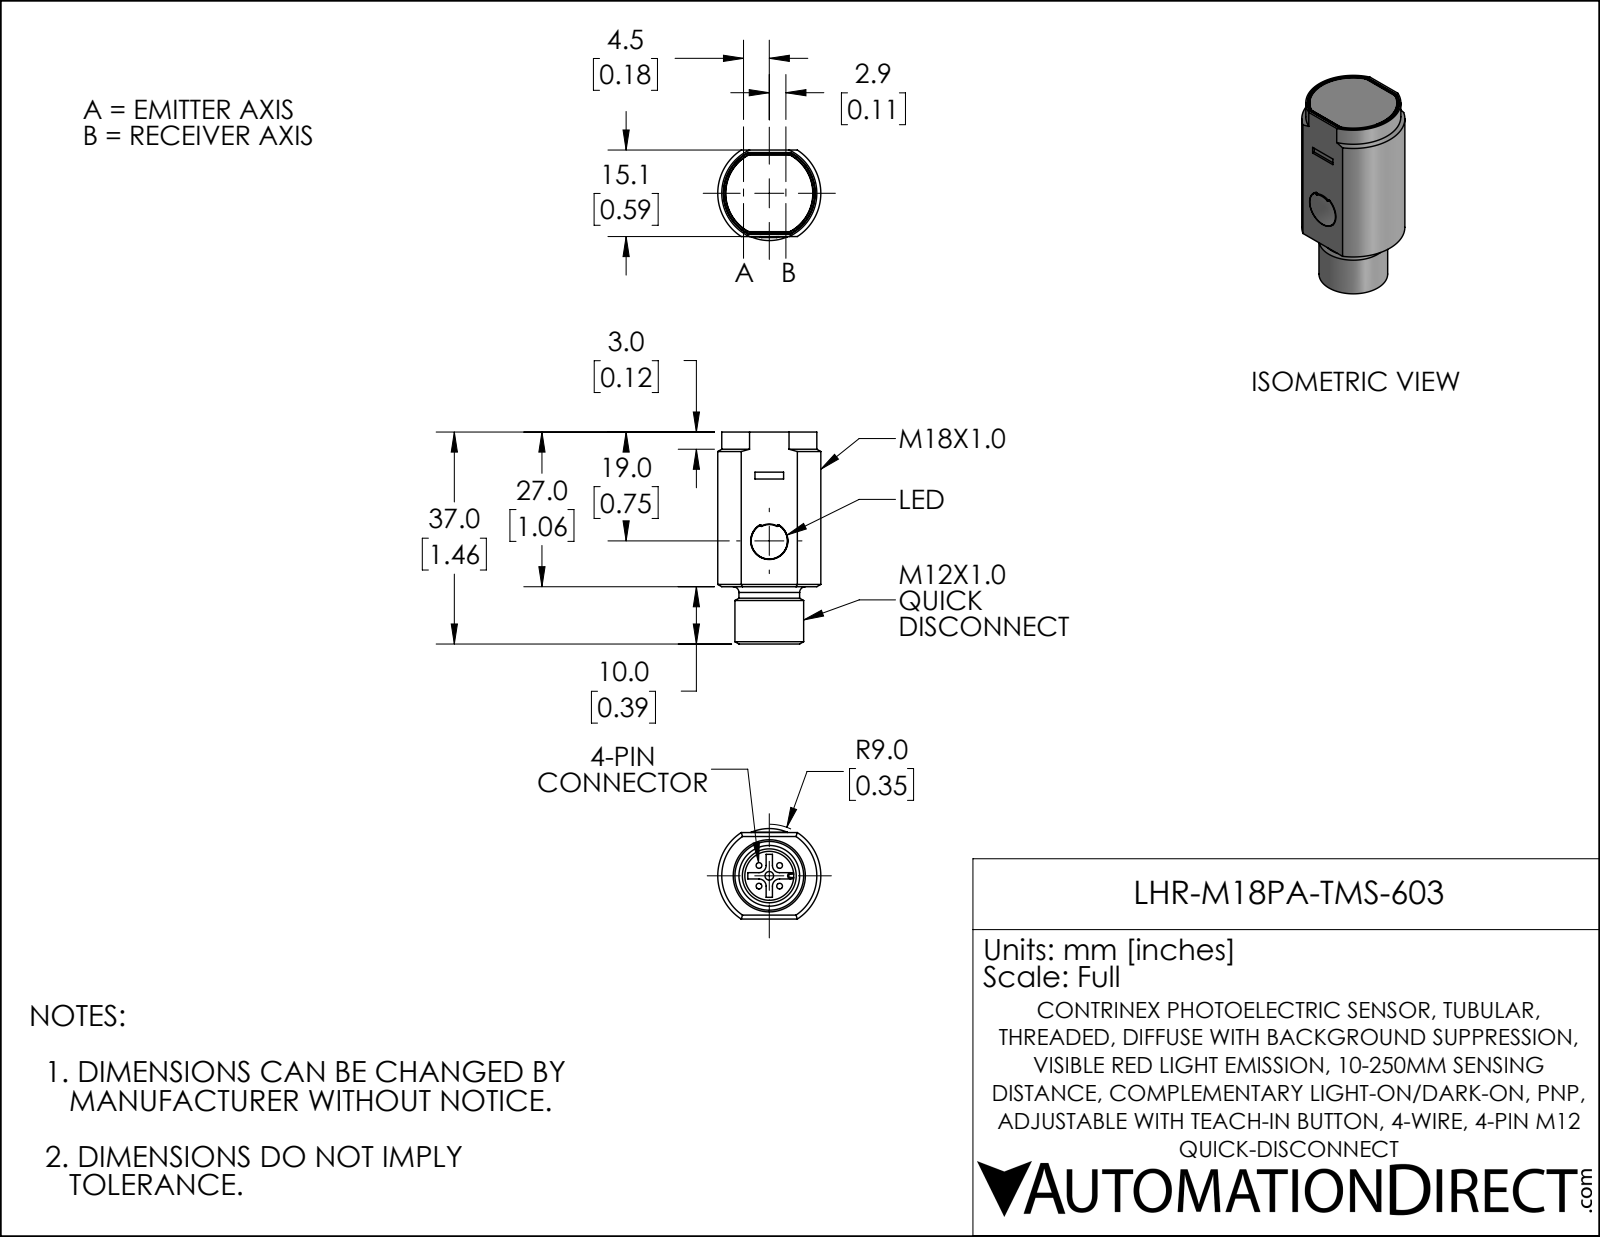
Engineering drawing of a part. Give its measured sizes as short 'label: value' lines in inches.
name: LHR-M18PA-TMS-603
written by: SolidWorks 2021 (AUTOMOTIVE_DESIGN)
unit: in
bodies: 1 solid, 125 faces (56 planar, 54 cylindrical, 15 other)
size: 1.457 × 0.709 × 0.622
volume: 0.418 in³; area: 4.241 in²
holes: 1× ⌀0.059, 1× ⌀0.256, 1× ⌀0.336
bosses: 4× ⌀0.039, 1× ⌀0.472, 1× ⌀0.417
rounds: 8× R0.006, 8× R0.014, 8× R0.028, 4× R0.049, 2× R0.008, 1× R0.02, 1× R0.112, 1× R0.116
face distances: 0.594, 1.061, 0.047, 1.108, 1.063, 1.11, 0.016, 1.457, 1.455, 0.394
